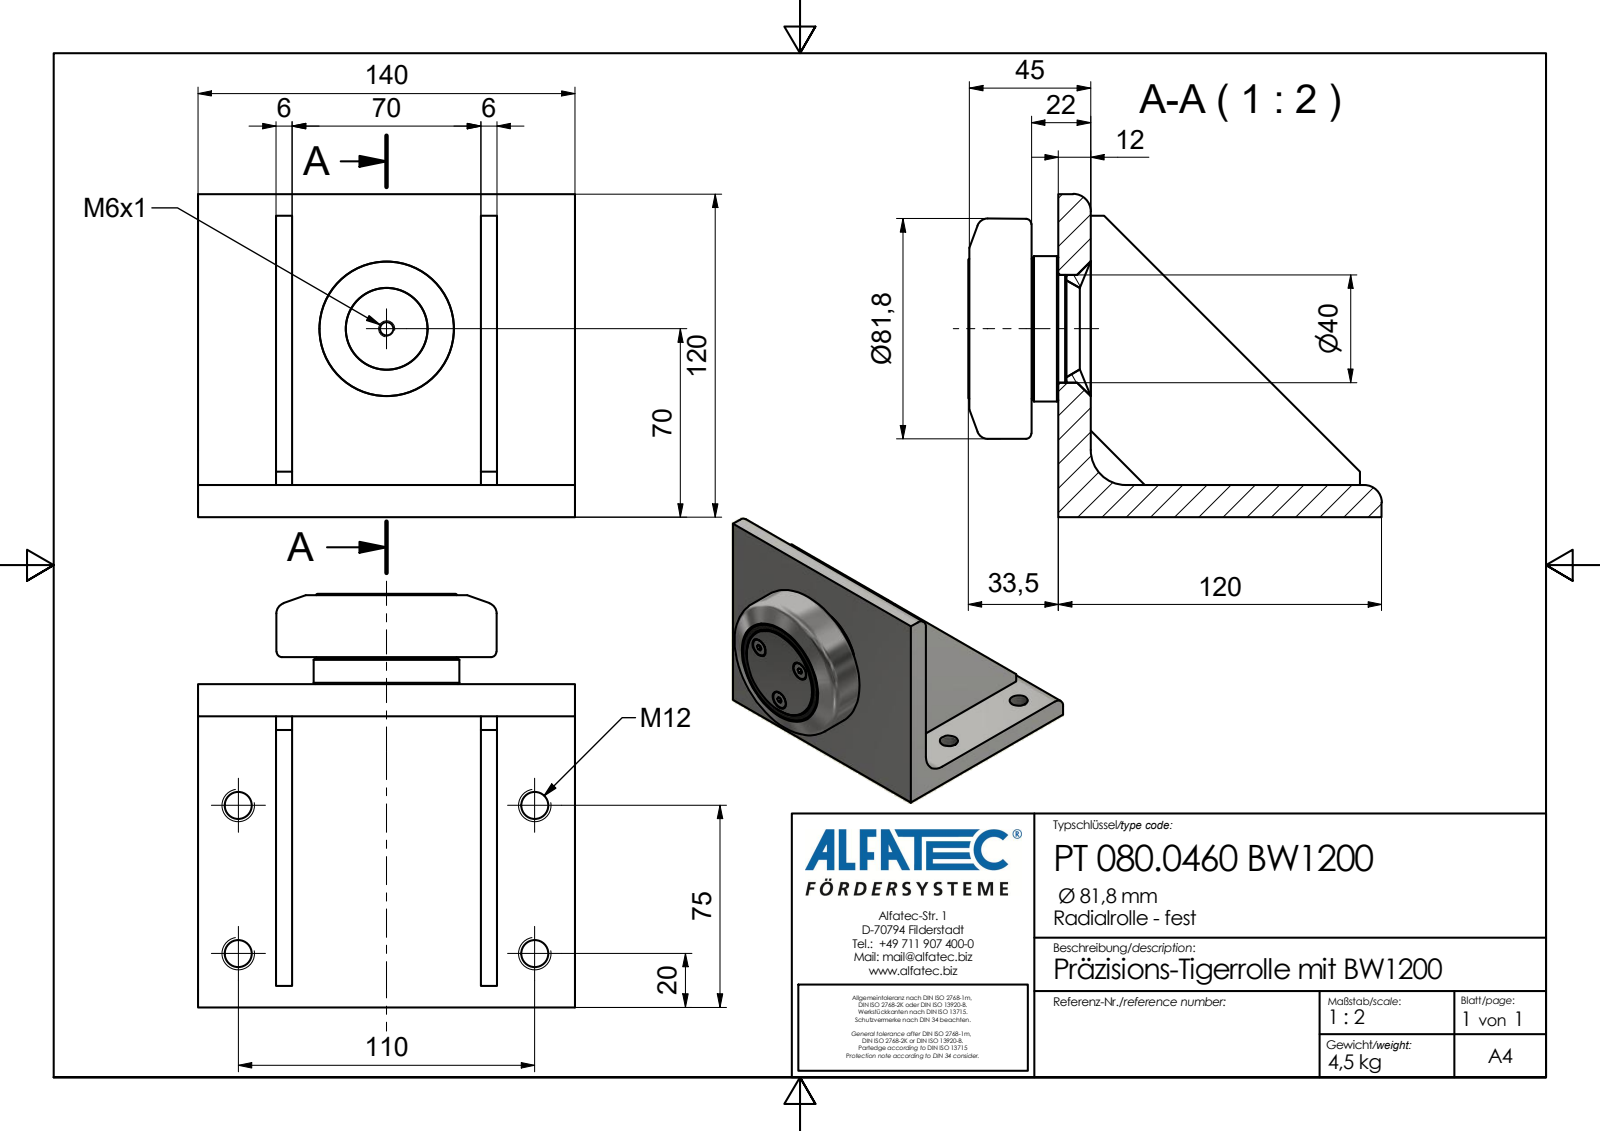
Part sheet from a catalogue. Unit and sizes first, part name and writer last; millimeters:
Units: millimetres
Overall size (bounding box): 153.5 × 140 × 120
Round holes (diameter × count): ⌀10.11 ×4, ⌀10.4 ×3, ⌀4.92 ×1
Round bosses / shafts (diameter × count): ⌀9.75 ×3, ⌀54 ×1, ⌀52 ×1
Partial cylindrical surfaces — rounded edges, fillets, slot ends (radius × count): R6.5 ×2, R13 ×1
Main face-to-face distances: 12, 76, 6, 29, 35, 105, 111, 70, 82, 140
Hole centre spacings: 18.5, 32.04, 55, 110, 122.98
Volume: 578 559 mm³ · Surface area: 106 490 mm²
Bodies: 1 solid, 78 faces (53 planar, 17 cylindrical, 8 other)
Part name (STEP PRODUCT): PT 080.0460 BW1200_Kontur
STEP written by: Autodesk Inventor 2020 (AP242_MANAGED_MODEL_BASED_3D_ENGINEERING_MIM_LF)
